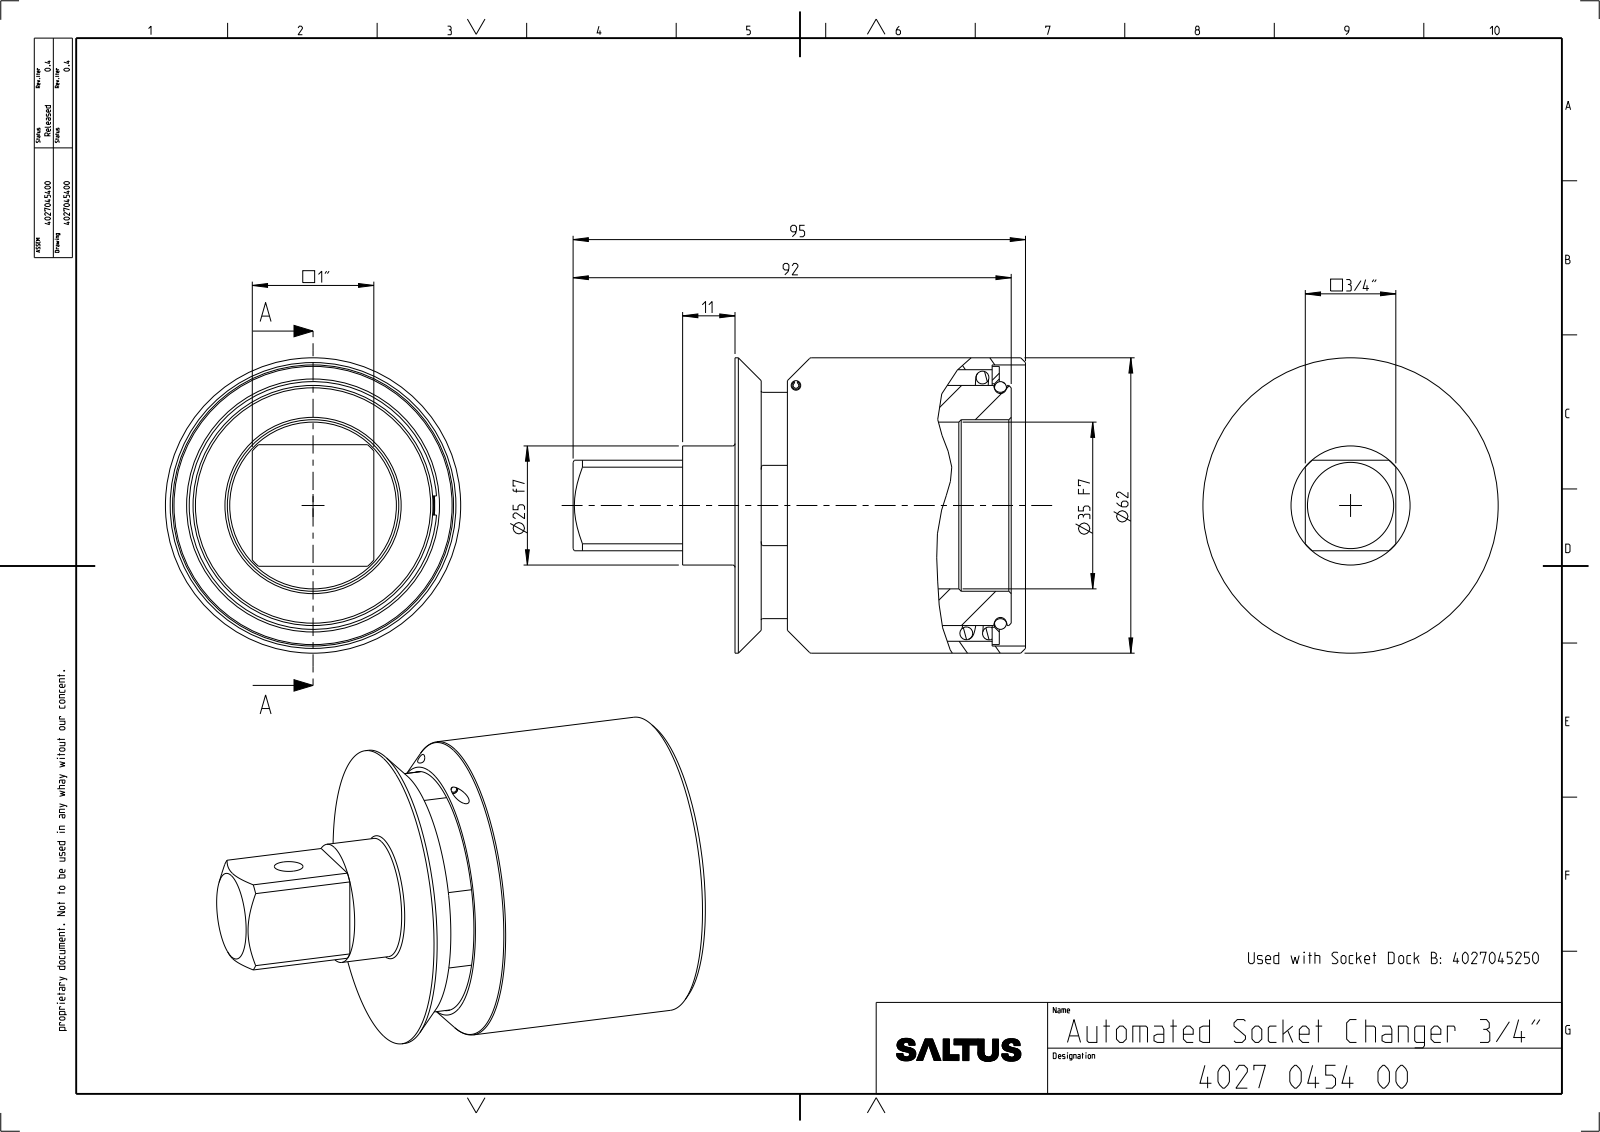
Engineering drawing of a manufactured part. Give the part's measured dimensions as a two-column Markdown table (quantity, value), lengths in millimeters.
| quantity | value |
| --- | --- |
| part name | 4027041519; 4027040211; 4027041386; 4027041390_AF2 (+4 more) |
| STEP written by | CREO PARAMETRIC BY PTC INC, 2022414 (CONFIG_CONTROL_DESIGN) |
| units | millimeters |
| bodies | 10 solids, 153 faces (41 planar, 58 cylindrical, 54 other) |
| overall size | 95 × 62 × 62 |
| volume | 122 263 mm³ |
| surface area | 52 680 mm² |
| round holes (diameter × count) | 1.2 × 1, 2 × 1, 6 × 1, 6.5 × 1, 7.1 × 1, 35 × 1, 36 × 1, 50.55 × 1, 51.1 × 1, 57 × 1, 58 × 1, 59 × 1 |
| round bosses / shafts (diameter × count) | 62 × 1, 58.4 × 1, 50.4 × 1, 25 × 1 |
| partial cylindrical surfaces (radius × count) | 0.3 × 8, 12.45 × 1, 17.15 × 1 |
| main face-to-face distances | 3.26, 22.26, 25.52, 54, 4, 58, 8.5, 19, 47, 49.5 |
| hole center spacings | 43.7 |
